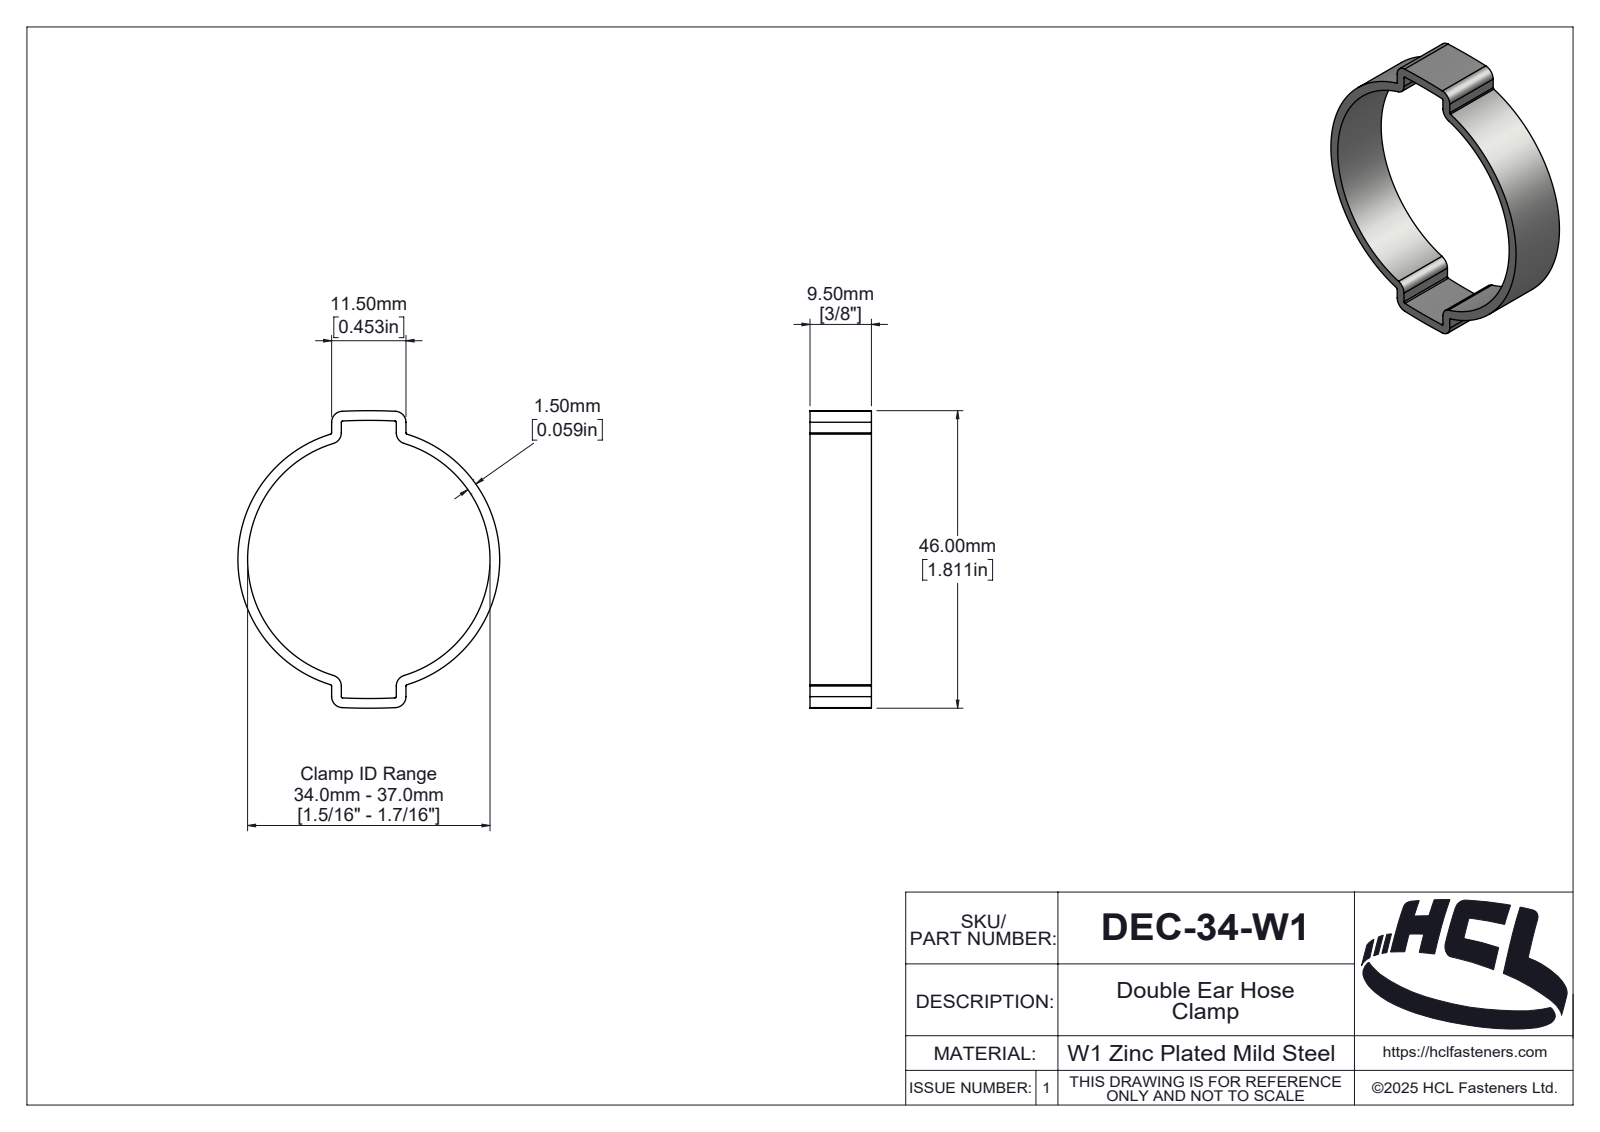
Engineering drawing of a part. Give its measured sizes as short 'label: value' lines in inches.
name: DEC-34-W1
written by: SolidWorks 2025 (AUTOMOTIVE_DESIGN)
unit: in
bodies: 1 solid, 137 faces (12 planar, 67 cylindrical, 58 other)
size: 1.811 × 1.594 × 0.374
volume: 0.116 in³; area: 4.546 in²
holes: 1× ⌀1.476
bosses: 1× ⌀1.594
rounds: 8× R0.008, 8× R0.067, 2× R3.557, 2× R3.617, 1× R0.011, 1× R0.044, 1× R0.056, 1× R0.059
face distances: 0.374, 0.059, 0.394, 0.453, 0.335, 0.22, 0.161, 0.174, 0.233, 0.212
